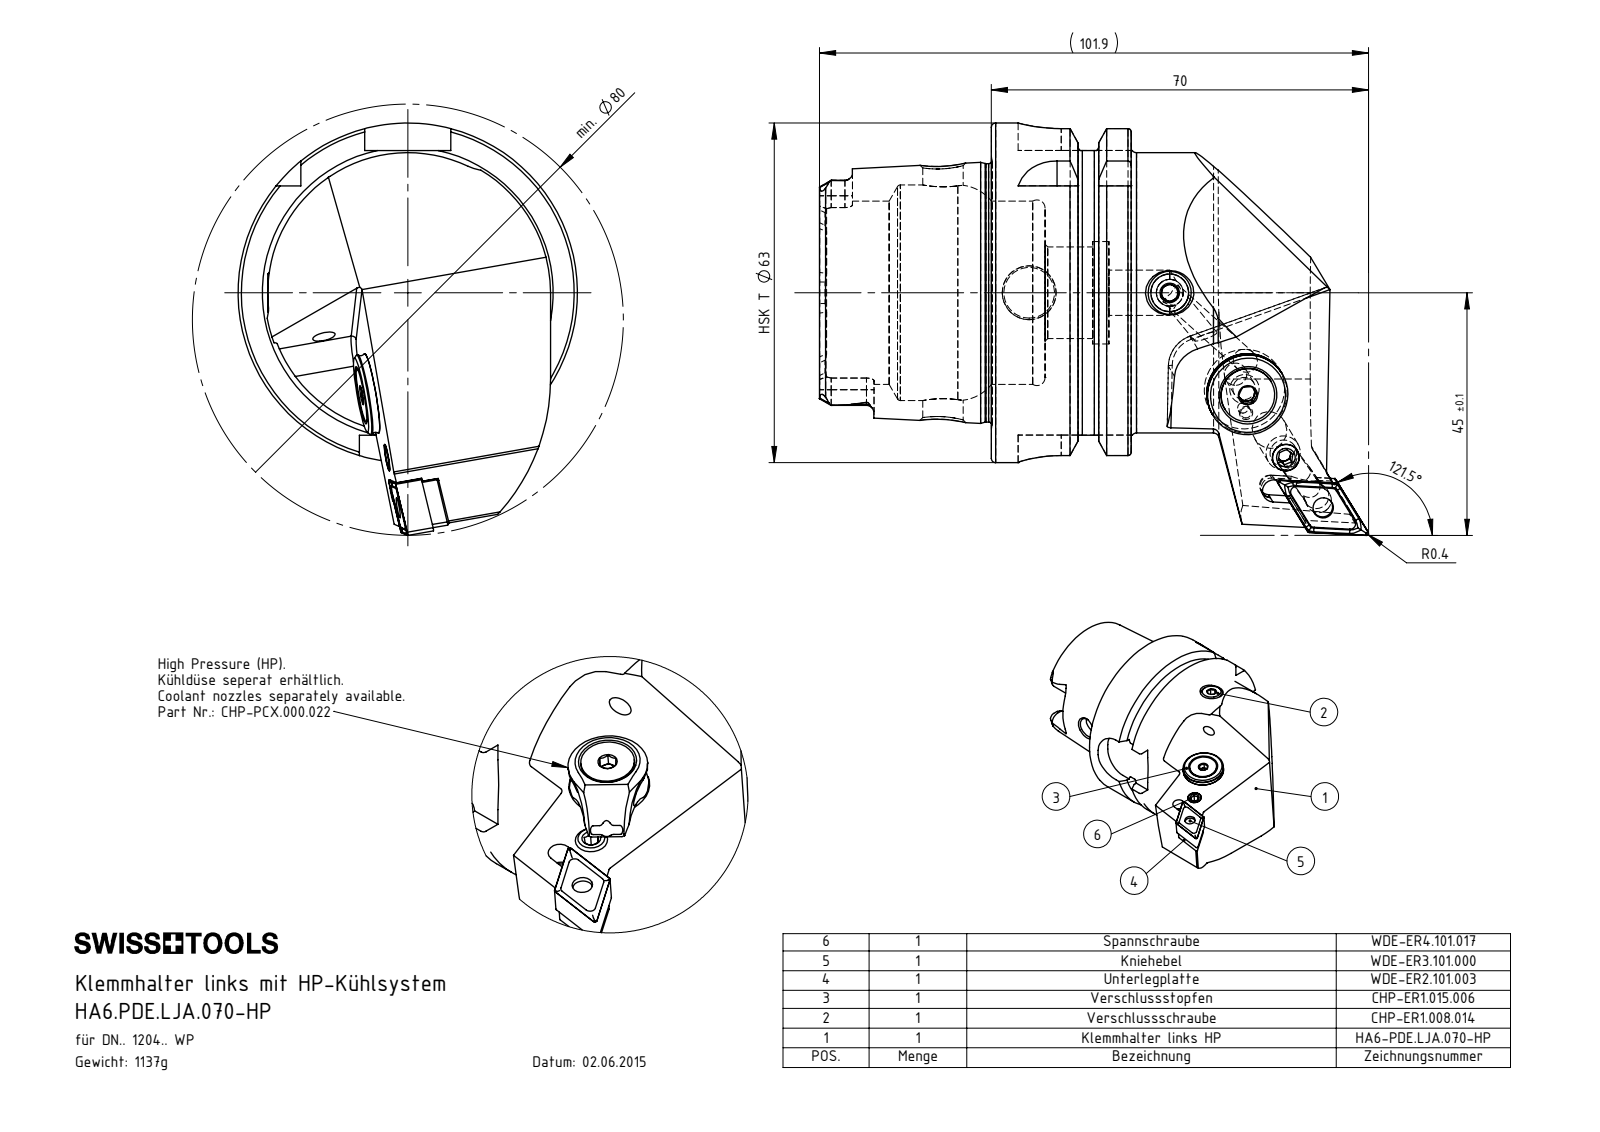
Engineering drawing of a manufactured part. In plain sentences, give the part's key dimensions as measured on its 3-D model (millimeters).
The part is named "WDE-ER1.101.000; DNMG110404; WDE-ER4.101.017_A; DIN 7991 - M5x15 (+8 more)". Its 3-D file was written by "SolidWorks 2017 (AUTOMOTIVE_DESIGN)". It is 11 solids with 397 faces: 175 planar, 86 cylindrical and 136 other. Overall it measures 101.91 by 76.5 by 63 millimeters. Its volume is 145 075 cubic millimeters and its surface area 34 360 square millimeters. Round holes: 3 of diameter 4.2, 2 of diameter 2.5, 2 of diameter 5, 1 of diameter 1.2, 1 of diameter 2, 1 of diameter 3, 1 of diameter 3.81, 1 of diameter 4.8, 1 of diameter 5.2, 1 of diameter 6.4, 1 of diameter 7, 1 of diameter 7.5. Round bosses or shafts: 1 of diameter 63, 1 of diameter 54.95, 1 of diameter 52, 1 of diameter 47.94, 1 of diameter 15, 1 of diameter 13.4, 1 of diameter 10, 1 of diameter 8. Partial cylindrical surfaces (rounded edges, fillets, slot ends): 8 of radius 0.4, 6 of radius 1.4, 4 of radius 2.1, 4 of radius 2.88, 4 of radius 8, 3 of radius 0.8, 1 of radius 1.83, 1 of radius 1.85. The main face-to-face distances are 25.95, 16, 9.95, 31.9, 41.85, 57.85, 52.8, 21.8, 11.85, 4.5. The hole center spacings are 10.41, 11.8, 14.23, 14.24, 26.01, 4.5, 4.51, 4.52.
